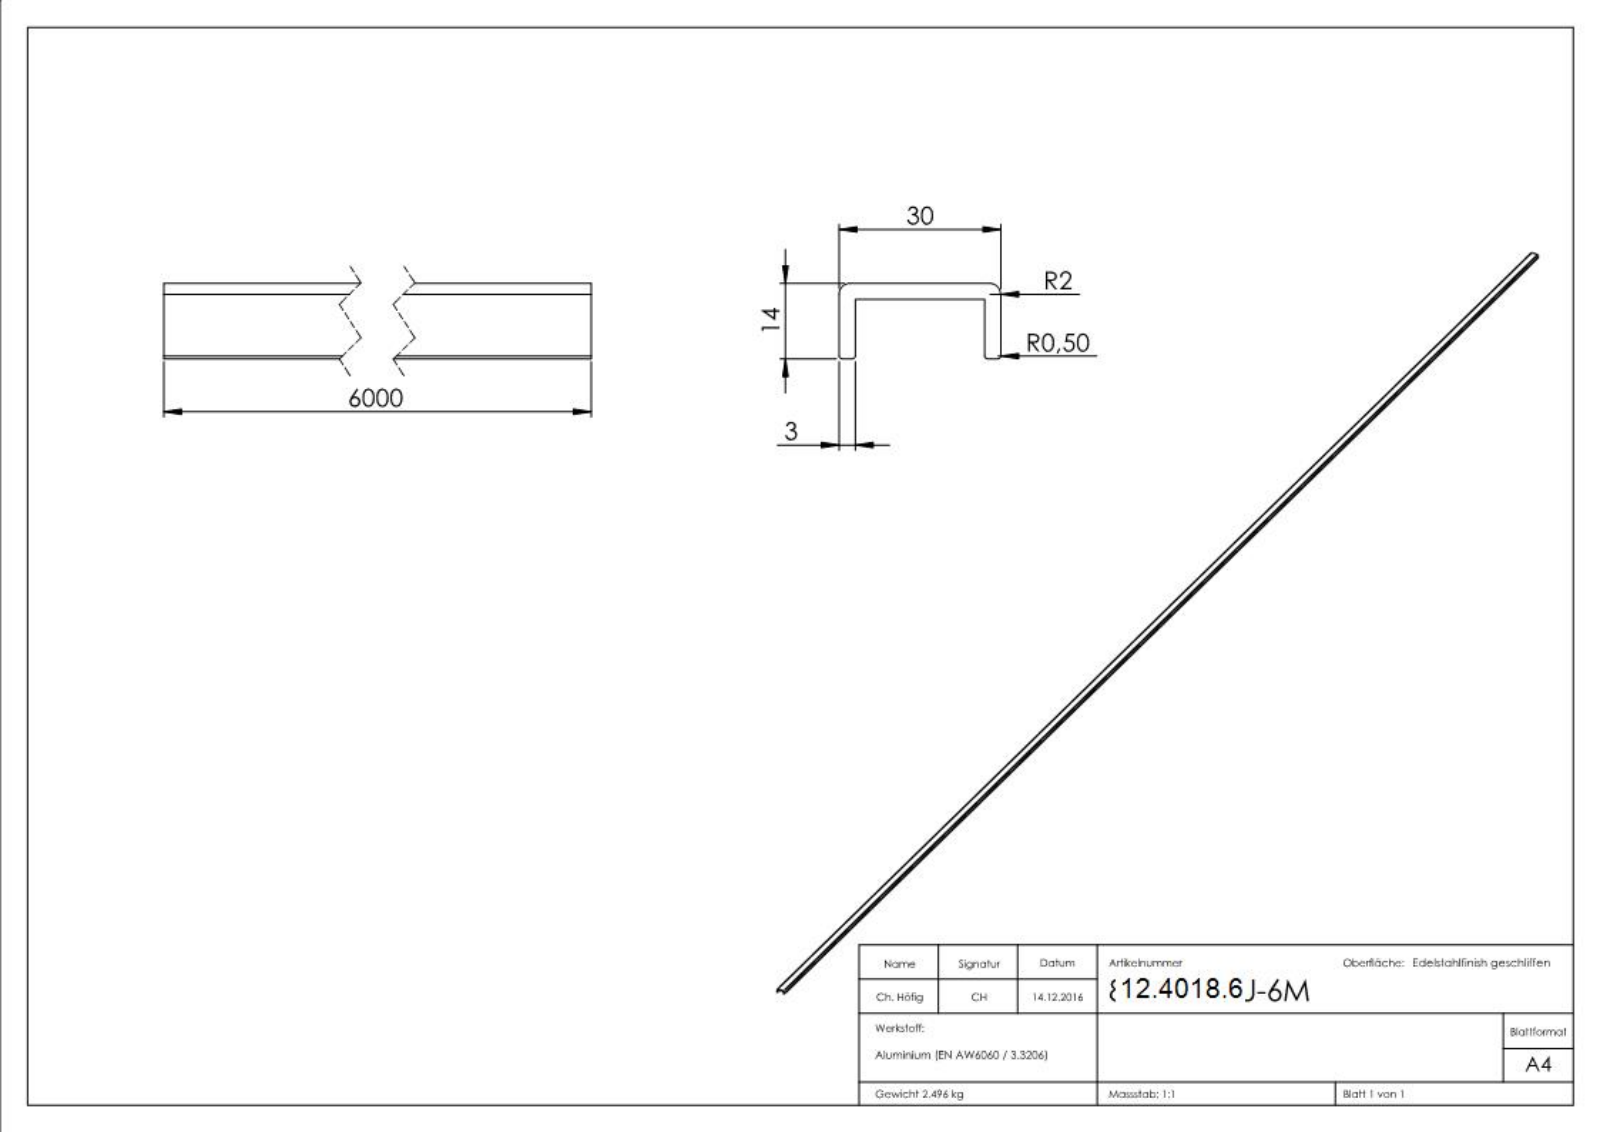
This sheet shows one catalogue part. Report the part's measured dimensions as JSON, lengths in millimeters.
{"part_name": "80539-ALU-6M", "step_written_by": "SolidWorks 2015 (CONFIG_CONTROL_DESIGN)", "units": "millimeters", "bodies": {"solids": 1, "faces": 283, "planar": 151, "cylindrical": 6, "other": 126}, "overall_size": [6000, 30, 14], "volume_mm3": 924411, "surface_area_mm2": 644868, "partial_cylinders_radius": [[0.5, 4], [2, 2]], "face_to_face_distances": [3, 27, 30, 24, 11, 14, 6000, 2.9, 24.1, 27.1]}
